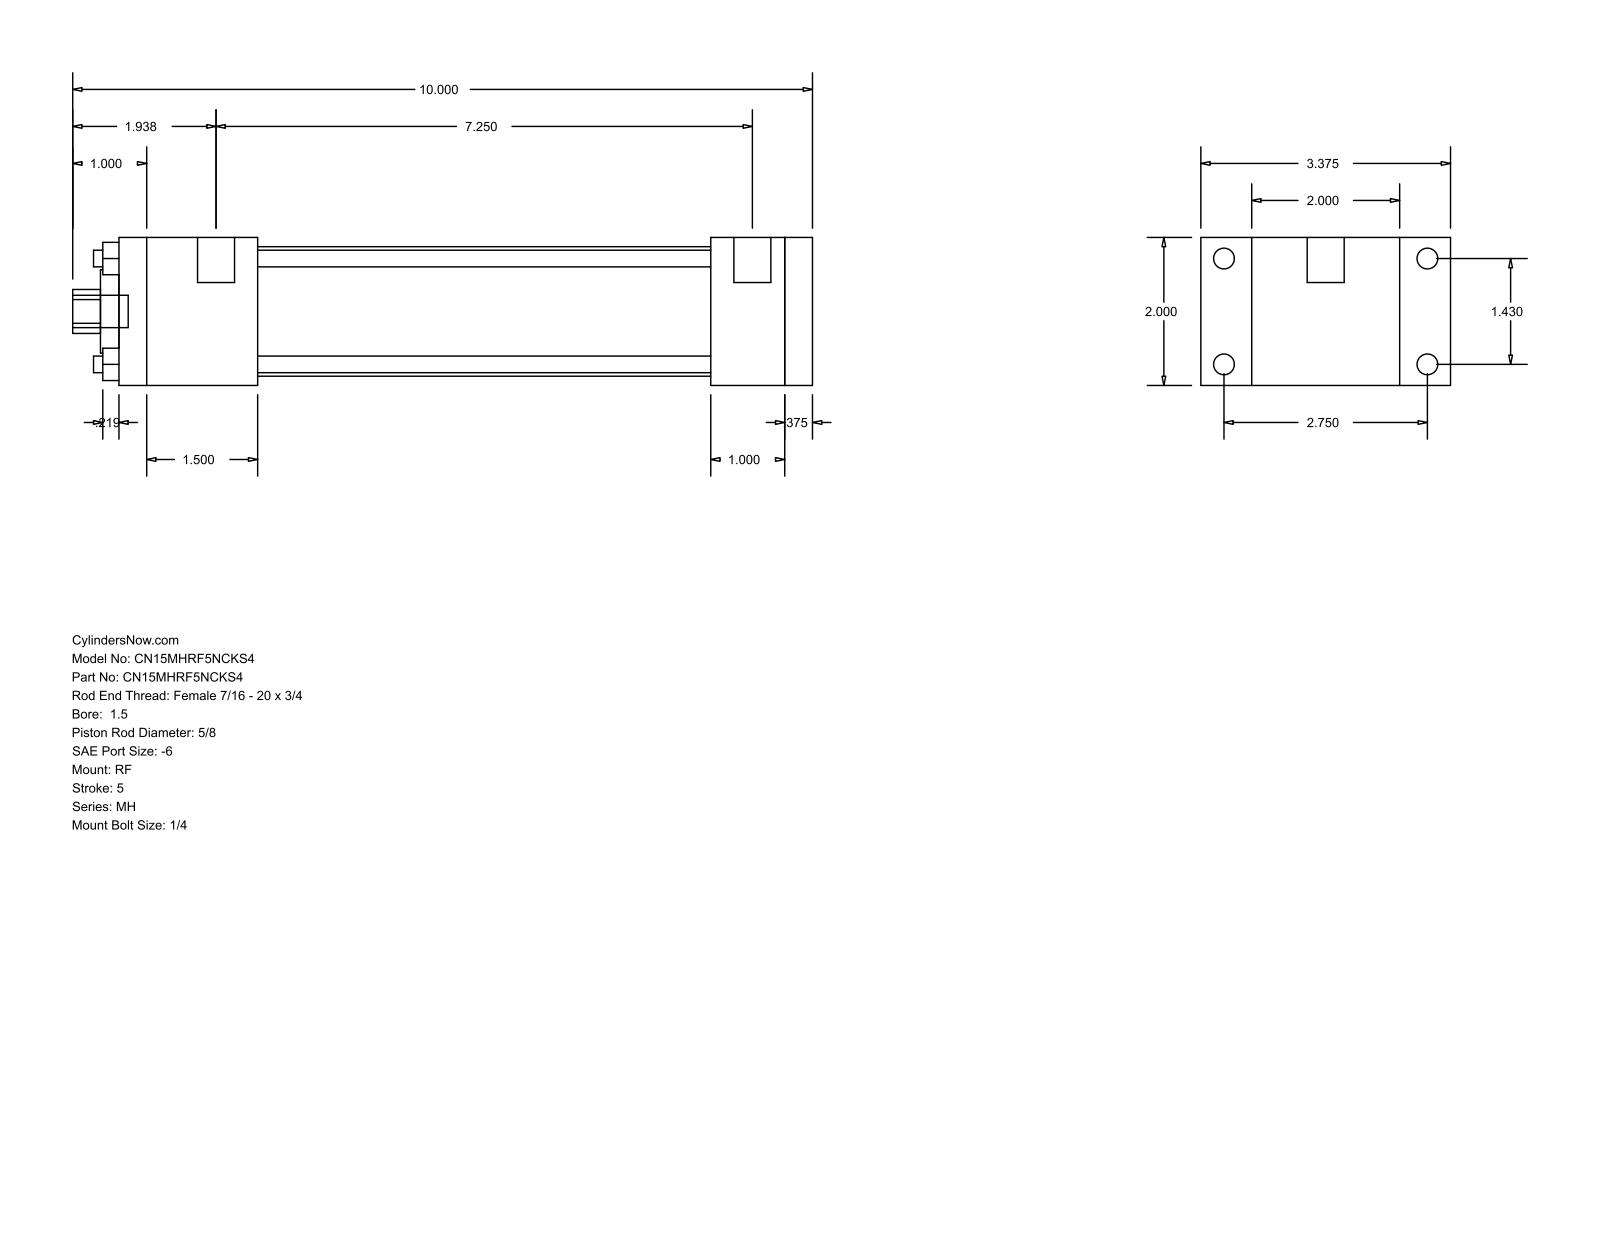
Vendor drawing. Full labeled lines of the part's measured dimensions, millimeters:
Part name (STEP PRODUCT): MH_RF__0150_0.625
STEP written by: GSSL Pune (CONFIG_CONTROL_DESIGN)
Units: millimetres
Bodies: 0 solids, 92 faces (64 planar, 28 cylindrical, 0 other)
Overall size (bounding box): 254 × 85.72 × 50.8
Round holes (diameter × count): ⌀5.71 ×4, ⌀15.88 ×1, ⌀28.57 ×1, ⌀44.45 ×1
Round bosses / shafts (diameter × count): ⌀7.14 ×4, ⌀5.56 ×4, ⌀12.7 ×2, ⌀11.11 ×1
Partial cylindrical surfaces — rounded edges, fillets, slot ends (radius × count): R7.54 ×1
Main face-to-face distances: 50.8, 9.53, 238.12, 228.59, 17.46, 68.26, 203.19, 25.4, 34.93, 47.62
Hole centre spacings: 25.68, 36.32, 51.36
